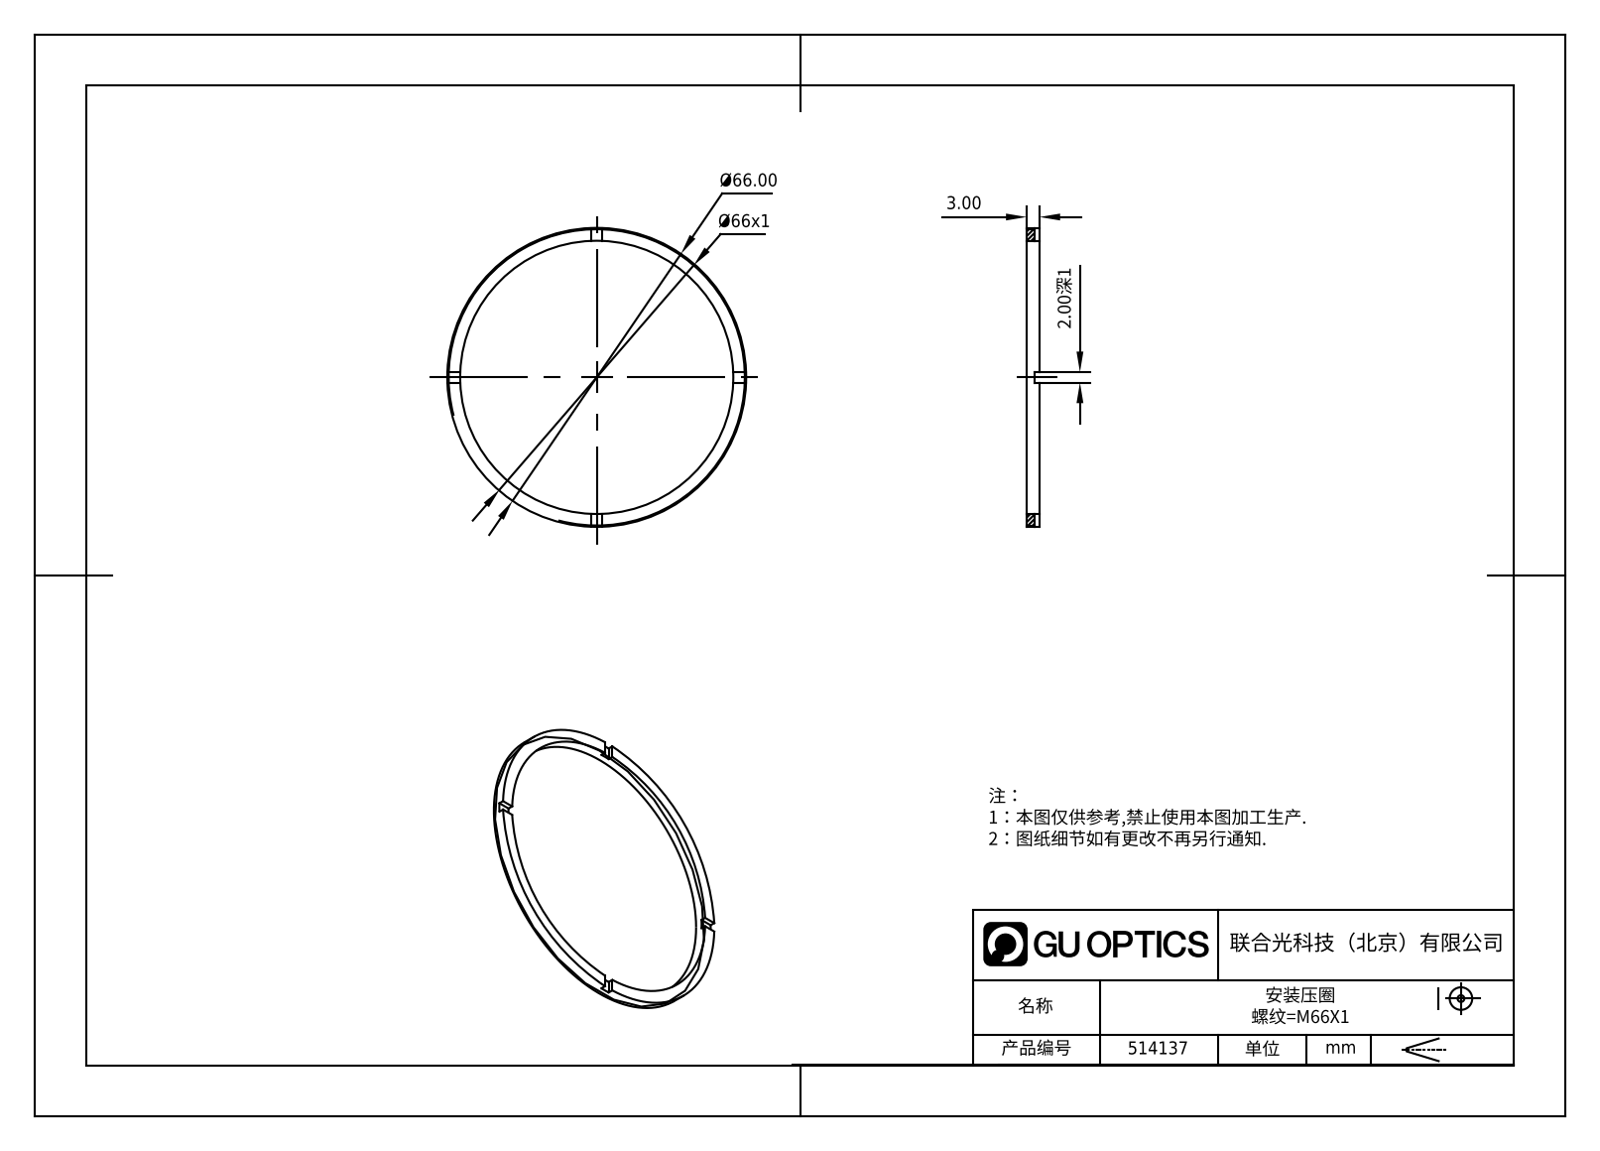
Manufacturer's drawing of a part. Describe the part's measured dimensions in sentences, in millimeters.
The part is named "514137". Its 3-D file was written by "SolidWorks 2020 (CONFIG_CONTROL_DESIGN)". It is 1 solid with 21 faces: 17 planar, 4 cylindrical and 0 other. Overall it measures 66 by 66 by 3 millimeters. Its volume is 1 476 cubic millimeters and its surface area 2 198 square millimeters. Round holes: 1 of diameter 61. Round bosses or shafts: 1 of diameter 66. The main face-to-face distances are 3, 2, 1.
